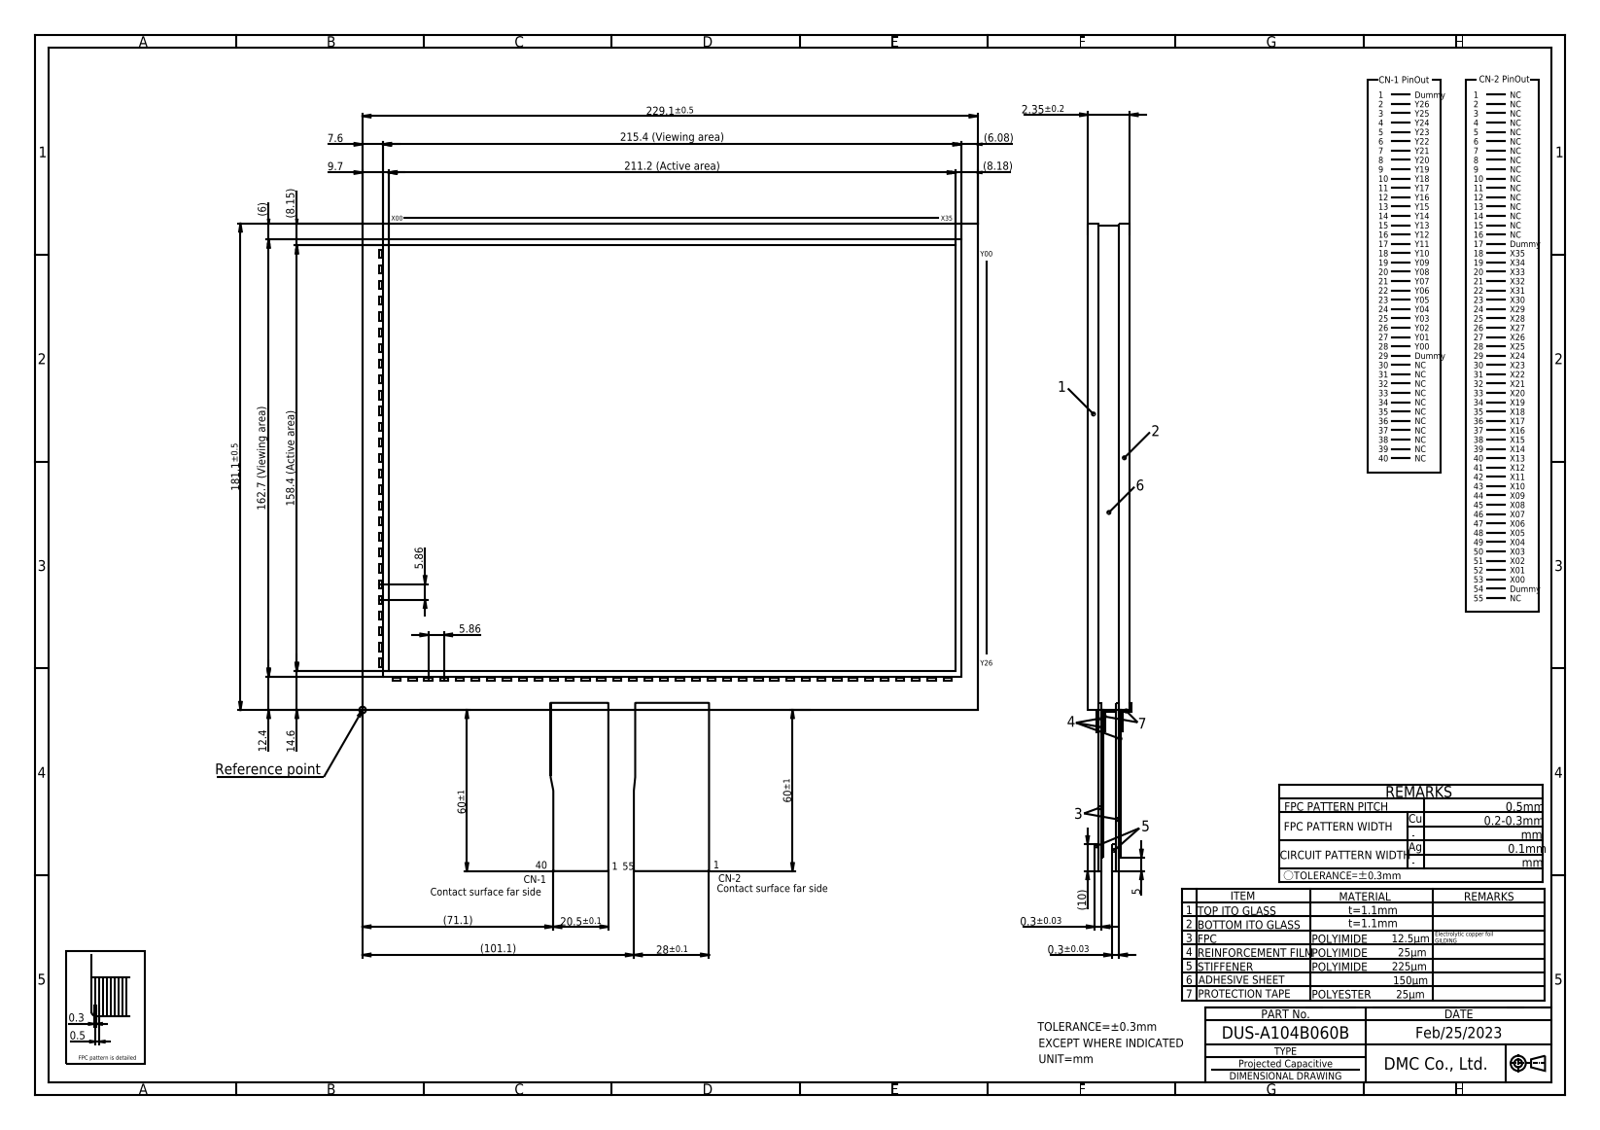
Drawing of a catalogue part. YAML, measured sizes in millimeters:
part_name: "DUS-A104B060B"
step_written_by: "Autodesk Inventor 2020 (CONFIG_CONTROL_DESIGN)"
units: millimeters
bodies: {solids: 1, faces: 422, planar: 418, cylindrical: 4, other: 0}
overall_size: [320.74, 277.32, 2.35]
volume: 97755
surface_area: 90977
partial_cylinders:
  - {radius: 0.2, count: 4}
face_to_face_distances: [2.35, 1.1, 1.15, 1.2, 1.25, 1, 2.25, 181.1, 0.8, 0.7]
